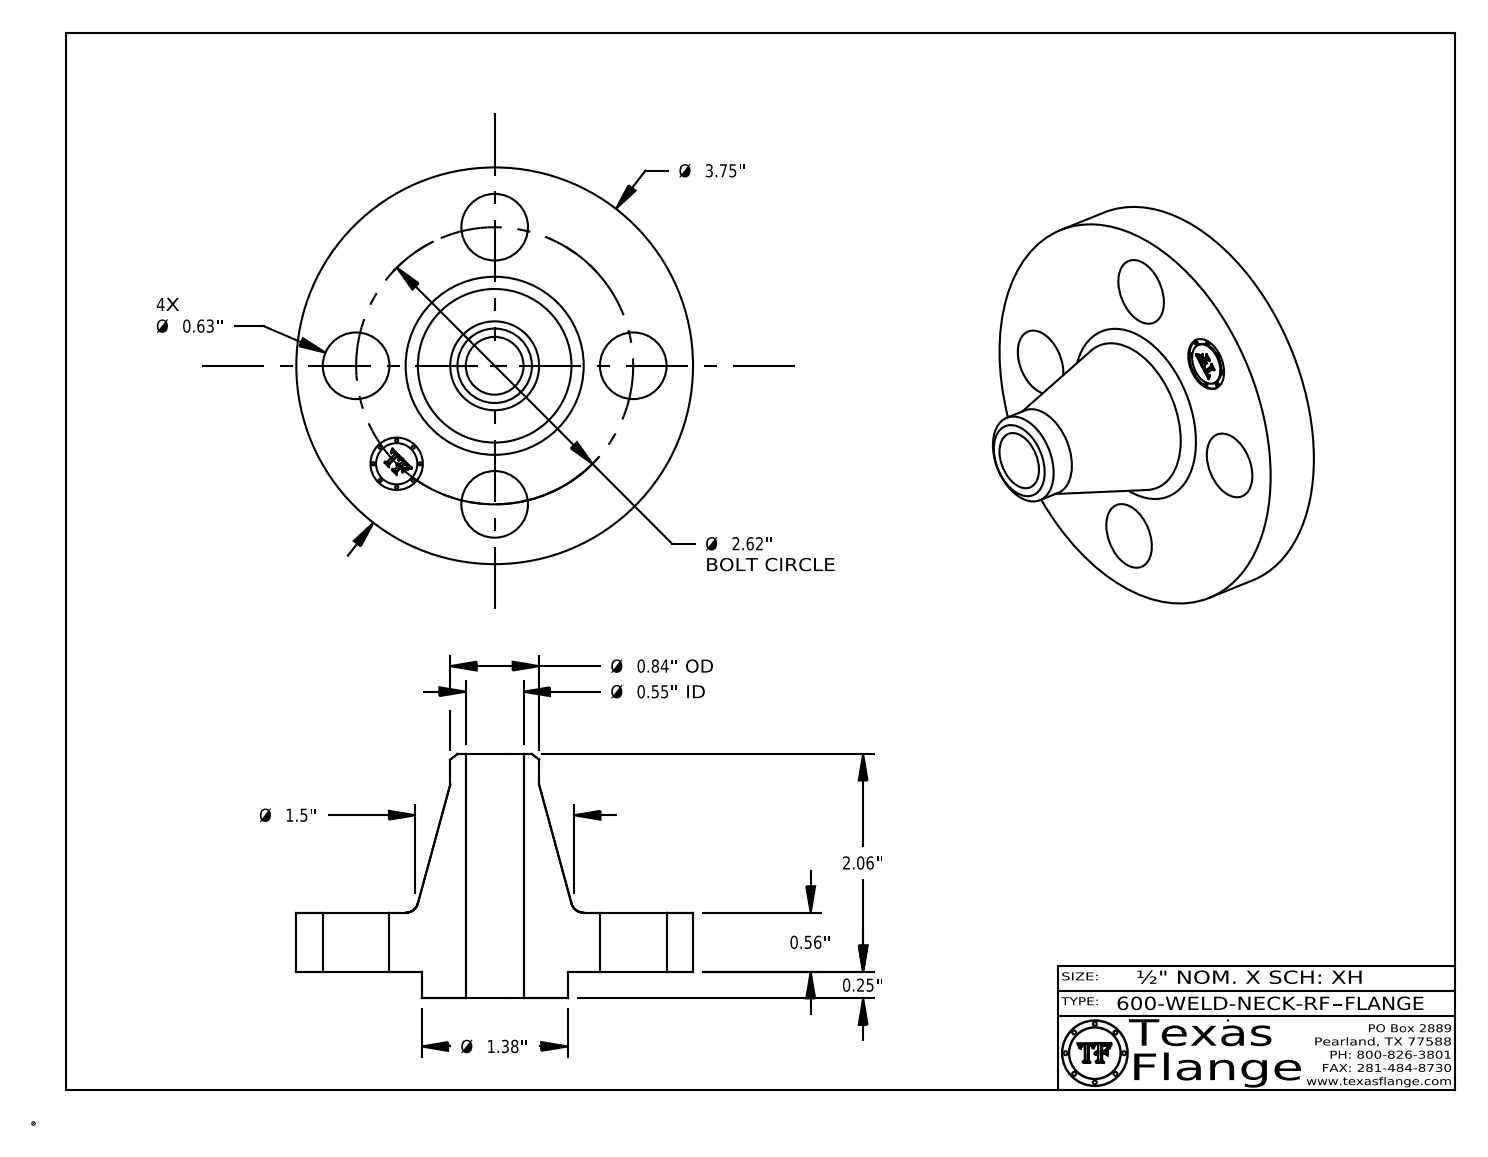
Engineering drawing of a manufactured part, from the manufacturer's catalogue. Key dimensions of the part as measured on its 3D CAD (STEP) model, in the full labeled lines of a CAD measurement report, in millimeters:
Part name (STEP PRODUCT): 600-WELD-NECK-RF
STEP written by: CATIA V5 STEP AP214 (AUTOMOTIVE_DESIGN)
Units: millimetres
Bodies: 1 solid, 411 faces (369 planar, 36 cylindrical, 6 other)
Overall size (bounding box): 95.3 × 95.3 × 58.7
Volume: 111 700 mm³ · Surface area: 25 320 mm²
Round holes (diameter × count): ⌀16 ×4, ⌀12.6 ×1, ⌀13.9 ×1
Round bosses / shafts (diameter × count): ⌀0.8 ×8, ⌀95.3 ×1, ⌀35.1 ×1, ⌀21.3 ×1, ⌀9.9 ×1
Main face-to-face distances: 14.2, 6.4, 20.6, 58.7, 52.3, 38.1, 20.2, 13.8, 0.4, 38.5
Hole centre spacings: 33.3, 47, 25.5, 61.5, 66.5, 33.3
